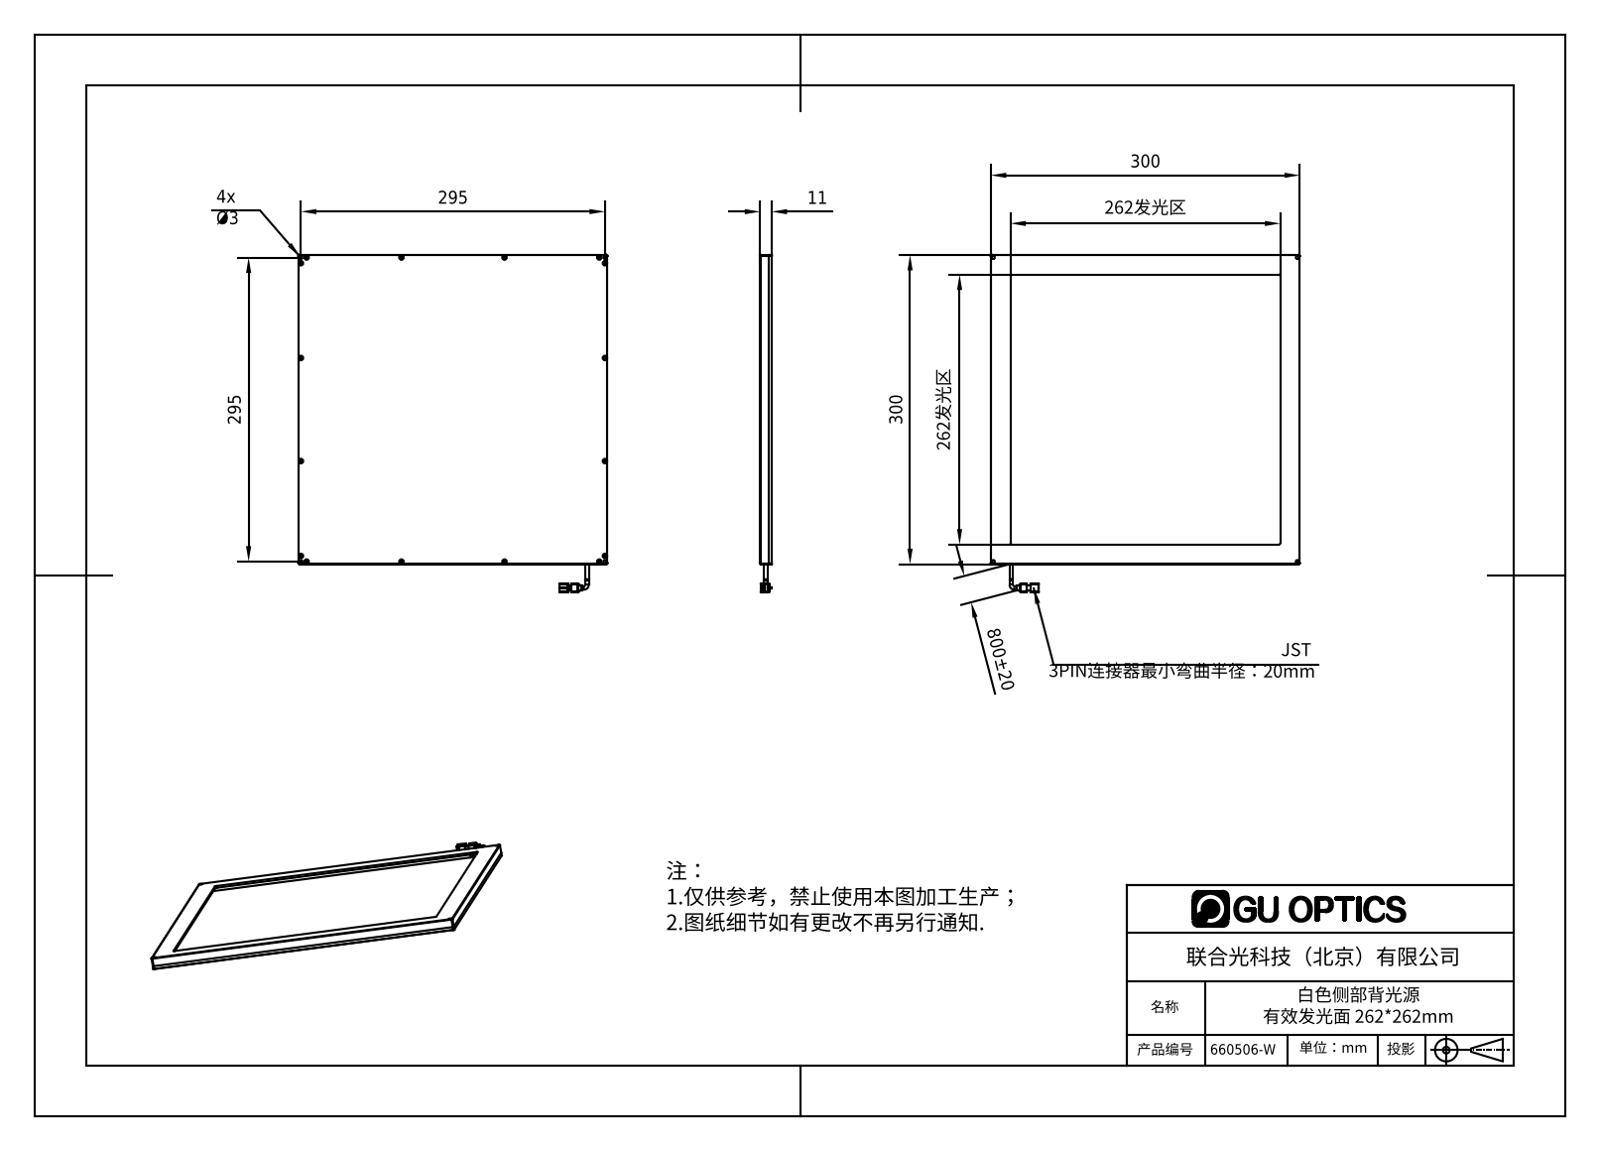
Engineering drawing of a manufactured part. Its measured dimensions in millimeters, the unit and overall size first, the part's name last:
Units: millimetres
Overall size (bounding box): 327 × 300 × 11
Round holes (diameter × count): ⌀1.6 ×16, ⌀2 ×16, ⌀2.4 ×16, ⌀3 ×4
Round bosses / shafts (diameter × count): ⌀3.5 ×2
Partial cylindrical surfaces — rounded edges, fillets, slot ends (radius × count): R0.5 ×10, R1 ×8, R1.5 ×4, R2 ×2
Main face-to-face distances: 3, 8, 11, 1.8, 6.2, 9.2, 4, 296, 300, 292
Hole centre spacings: 295, 5.5, 92, 97.5, 97.66, 192, 197.5, 197.58
Volume: 337 644 mm³ · Surface area: 246 818 mm²
Bodies: 4 solids, 447 faces (176 planar, 146 cylindrical, 125 other)
Part name (STEP PRODUCT): 660506-W
STEP written by: SolidWorks 2016 (AUTOMOTIVE_DESIGN)
